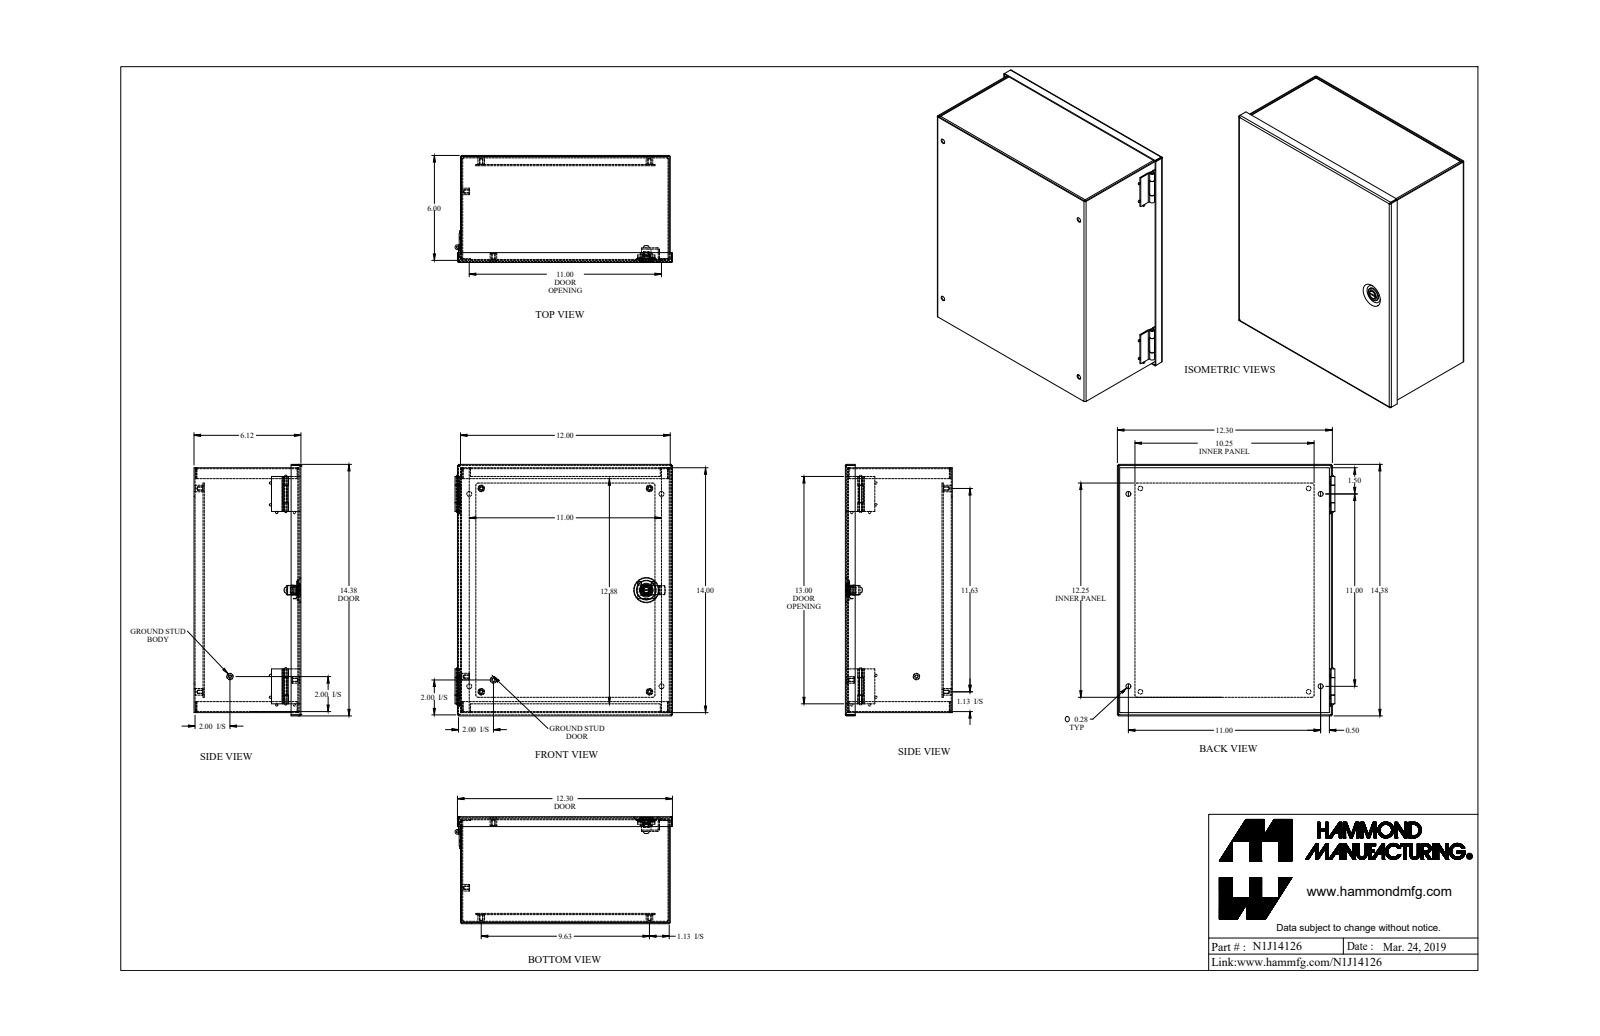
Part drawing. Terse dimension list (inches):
name: N1J14126
written by: SolidWorks 2018 (AUTOMOTIVE_DESIGN)
unit: in
bodies: 18 solids, 477 faces (224 planar, 188 cylindrical, 65 other)
size: 14.38 × 12.443 × 6.118
volume: 51.38 in³; area: 1 743 in²
holes: 6× ⌀0.156, 4× ⌀0.265, 4× ⌀0.28, 1× ⌀0.125, 1× ⌀0.319, 1× ⌀0.476
bosses: 8× ⌀0.131, 6× ⌀0.375, 1× ⌀0.787, 1× ⌀0.547, 1× ⌀0.472, 1× ⌀0.469, 1× ⌀0.366, 1× ⌀0.32
rounds: 16× R0.029, 16× R0.086, 4× R0.012, 4× R0.1, 4× R0.125, 2× R0.036, 2× R0.079, 2× R0.25
face distances: 0.057, 6.061, 6.004, 6.118, 11.943, 13.943, 0.072, 0.517, 0.46, 5.544
hole spacings: 0.755, 10.317, 11, 11.333, 15.307, 5.569, 5.815, 9.625
